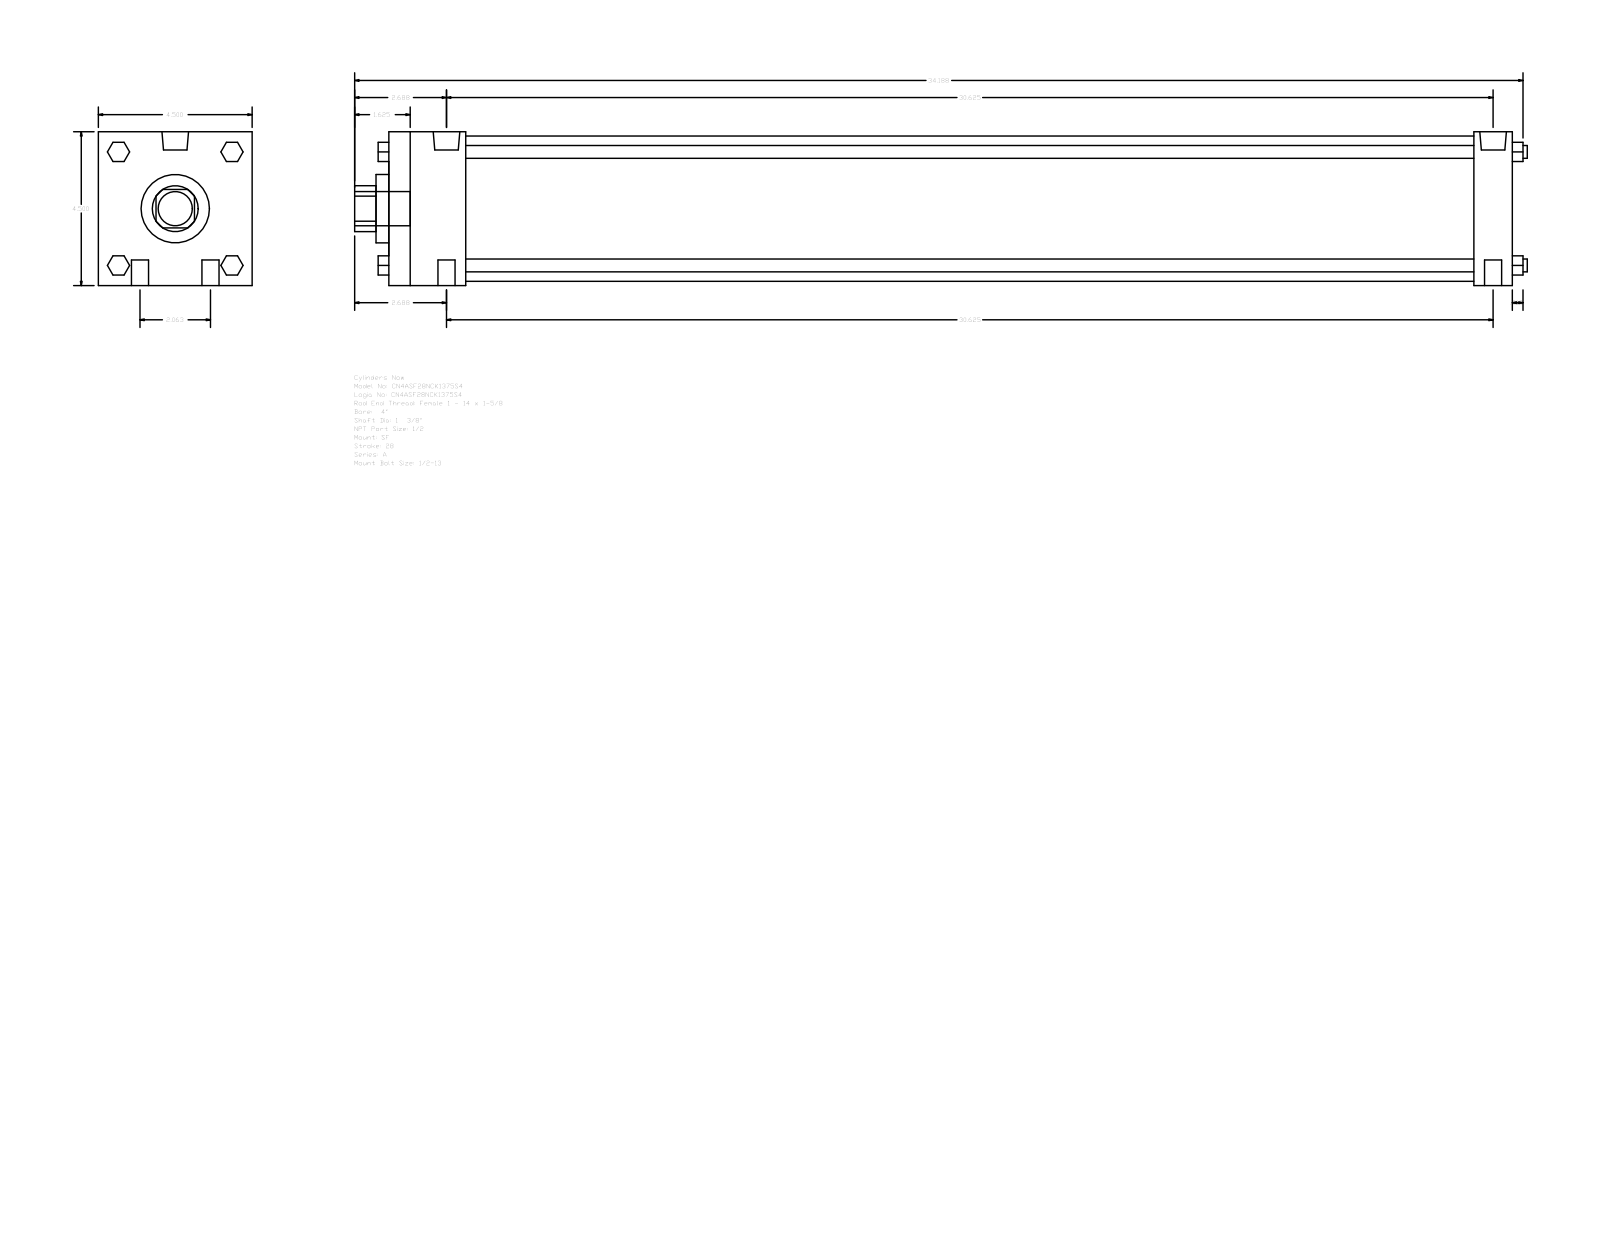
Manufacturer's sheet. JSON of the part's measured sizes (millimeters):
{"part_name": "A_SF__0400_1.375", "step_written_by": "GSSL Pune (CONFIG_CONTROL_DESIGN)", "units": "millimeters", "bodies": {"solids": 0, "faces": 124, "planar": 94, "cylindrical": 30, "other": 0}, "overall_size": [871.54, 114.3, 114.3], "round_holes": [[34.92, 1], [50.8, 1], [107.95, 1]], "round_bosses_or_shafts": [[12.7, 4], [9.53, 4], [19.77, 2], [8.73, 2], [25.4, 1]], "partial_cylinders_radius": [[17.06, 1]], "face_to_face_distances": [114.3, 835.02, 28.57, 806.45, 57.15, 749.3, 777.87, 14.29, 9.52, 66.67]}
